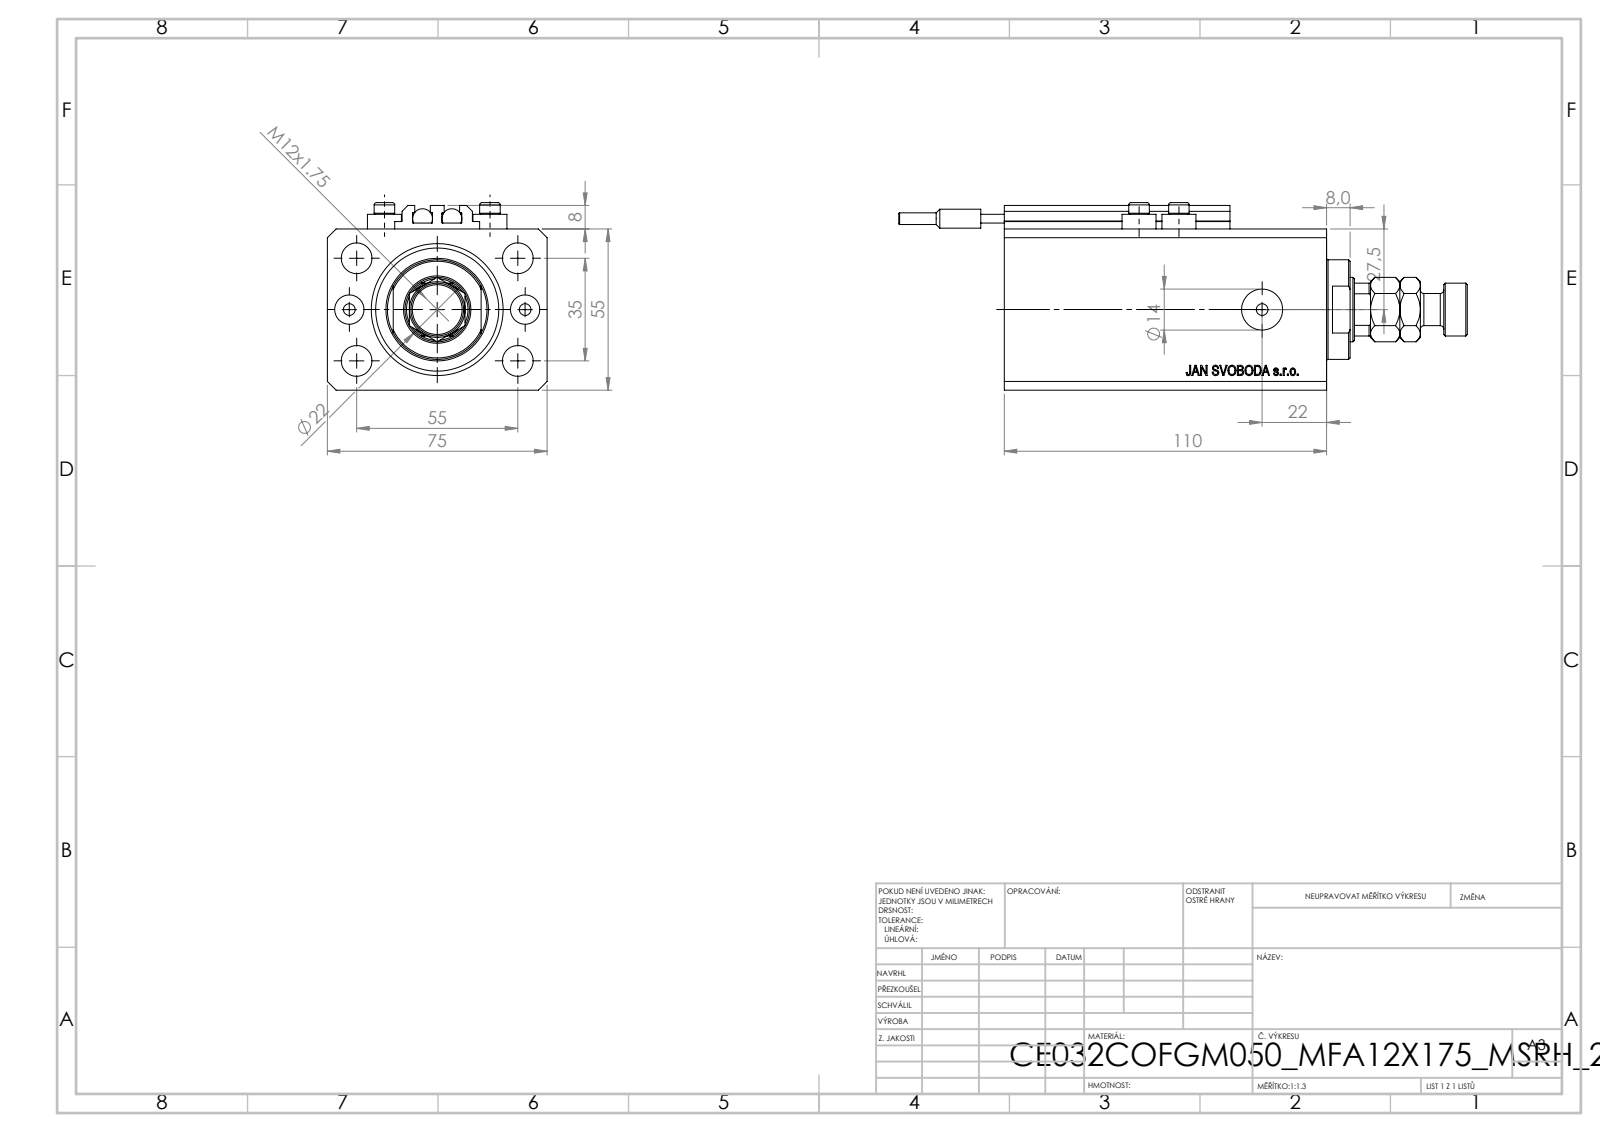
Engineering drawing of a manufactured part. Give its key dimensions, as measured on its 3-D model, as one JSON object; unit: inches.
{"part_name": "V250CE_C_VCP; V250CE_C_Body; SWITCH_V250CE; MFA (+2 more)", "step_written_by": "SolidWorks 2019 (CONFIG_CONTROL_DESIGN)", "units": "inches", "bodies": {"solids": 11, "faces": 1138, "planar": 552, "cylindrical": 102, "other": 484}, "overall_size": [7.638, 2.953, 2.52], "volume_in3": 25.66, "surface_area_in2": 149.7, "round_holes": [[0.157, 8], [0.413, 5], [0.394, 2], [0.551, 2], [0.866, 1], [1.26, 1], [1.772, 1]], "round_bosses_or_shafts": [[0.457, 4], [0.276, 4], [0.268, 2], [0.256, 2], [0.157, 2], [1.339, 1], [0.709, 1], [0.433, 1]], "partial_cylinders_radius": [[0.008, 10], [0.413, 1]], "face_to_face_distances": [2.165, 2.953, 4.331, 0.591, 3.74, 0.39, 0.118, 3.35, 3.941, 0.098], "hole_center_spacings": [0.696, 1.283, 2.366, 0.535, 1.181, 1.378, 1.417, 1.515]}
